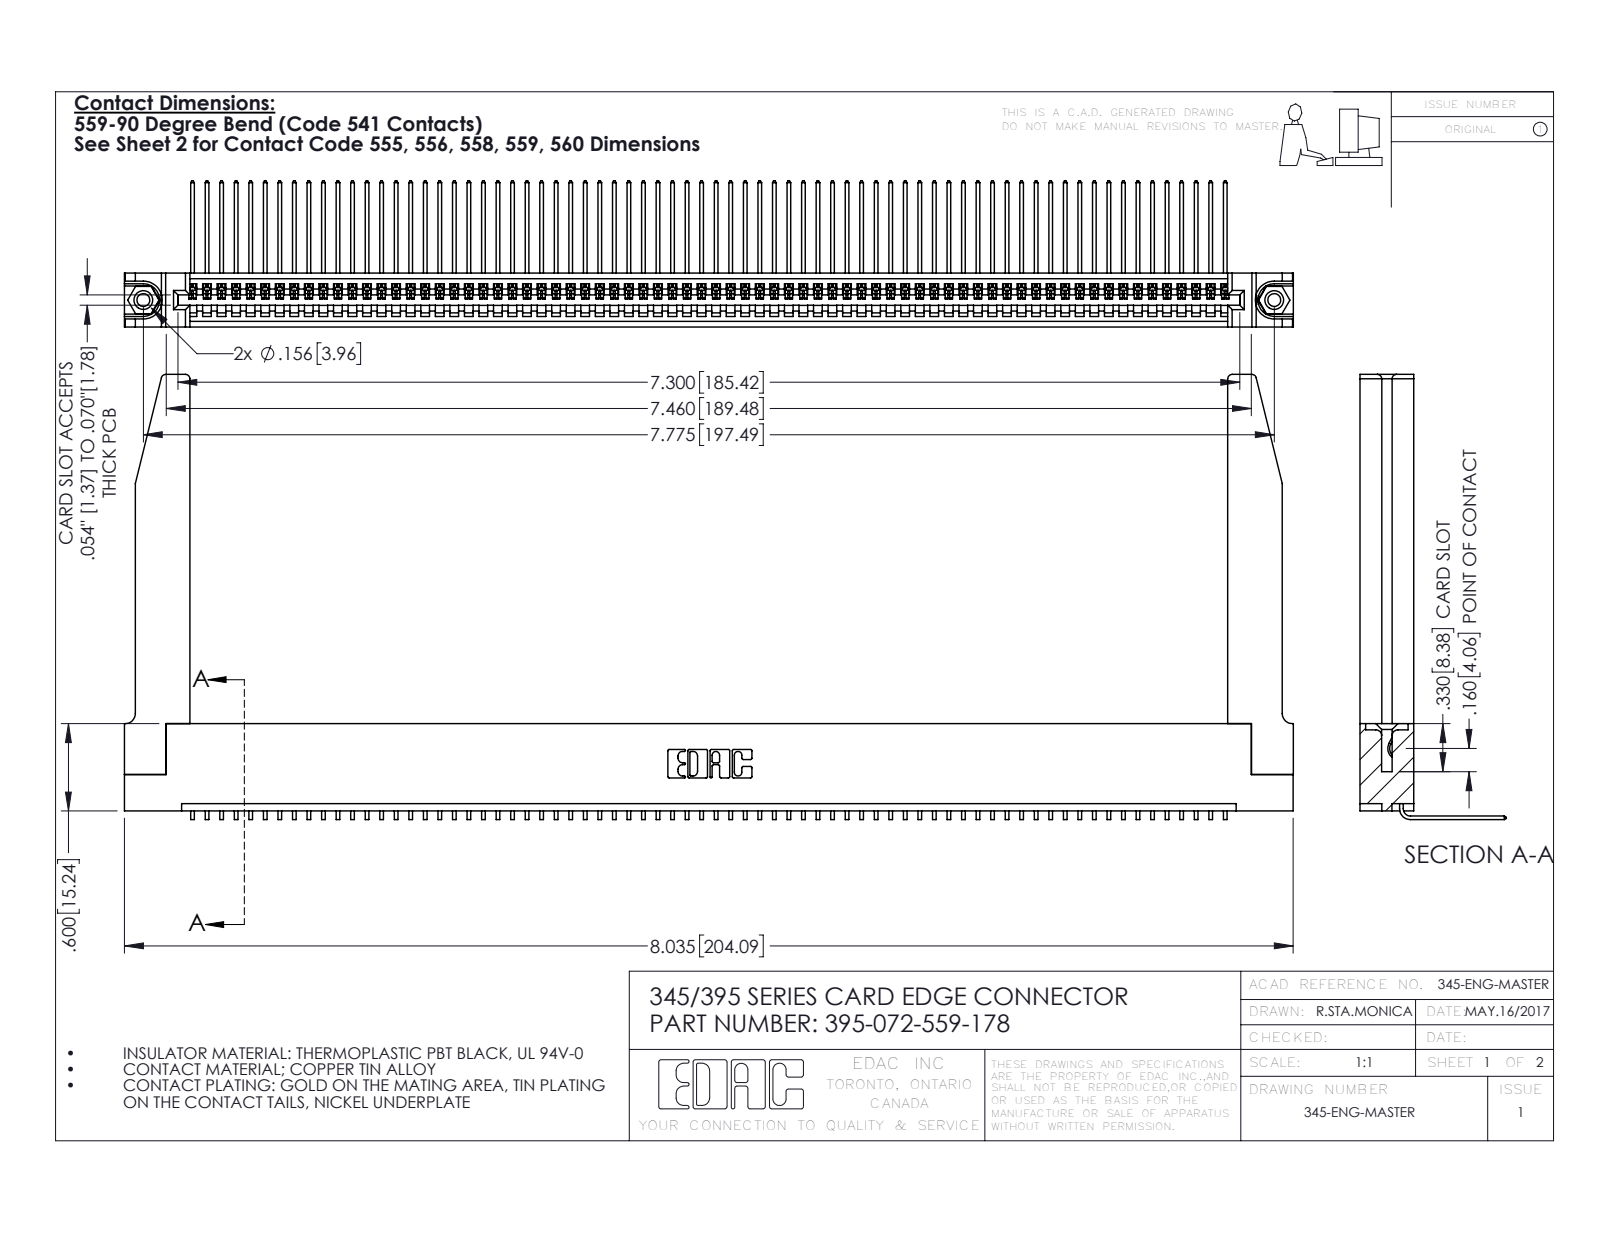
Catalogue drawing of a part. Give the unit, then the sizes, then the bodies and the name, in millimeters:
Units: millimetres
Overall size (bounding box): 204.1 × 77.7 × 25.5
Round holes (diameter × count): ⌀2.3 ×2, ⌀3.2 ×2, ⌀4 ×2, ⌀1.6 ×1
Round bosses / shafts (diameter × count): ⌀3.9 ×2
Partial cylindrical surfaces — rounded edges, fillets, slot ends (radius × count): R0.2 ×144, R0.3 ×22, R0.8 ×8, R0.2 ×6, R0.8 ×6, R0.7 ×3, R0.8 ×2, R1 ×2
Main face-to-face distances: 1.8, 9.4, 7.6, 5.1, 2.5, 6.9, 0.6, 5.7, 3.8, 3.8
Hole centre spacings: 6.9, 191.5, 197.5
Volume: 27 640 mm³ · Surface area: 35 070 mm²
Bodies: 77 solids, 4680 faces (3246 planar, 1382 cylindrical, 52 other)
Part name (STEP PRODUCT): 395-072-559-178; 345-292-001_558 559 Tail - 1; 345 Part_Flush Mounting Lugs - 0.156 Dia-TH; 345-220-078_345-220-078 (+1 more)
STEP written by: SolidWorks 2016 (CONFIG_CONTROL_DESIGN)
